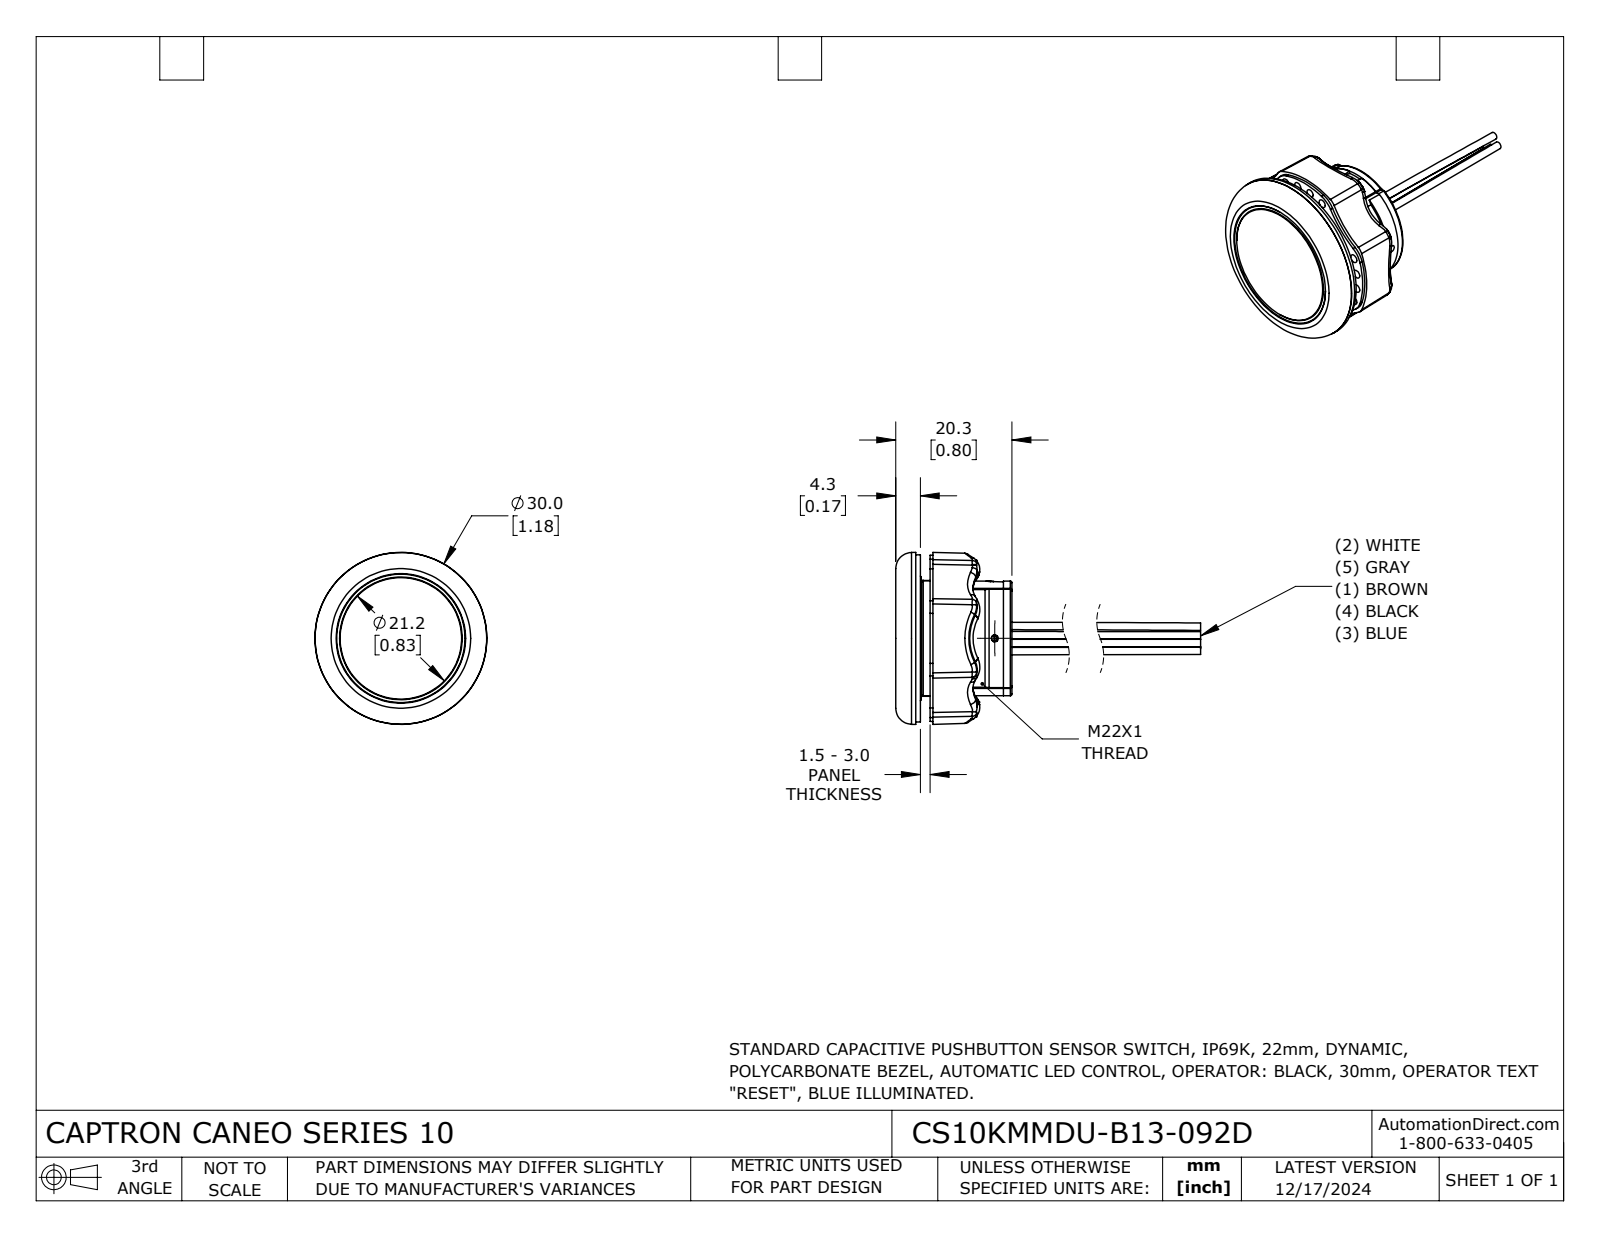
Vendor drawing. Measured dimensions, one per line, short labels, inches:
name: CS10KMMDU-B13-092D
written by: SolidWorks 2024 (CONFIG_CONTROL_DESIGN)
unit: in
bodies: 7 solids, 601 faces (204 planar, 75 cylindrical, 322 other)
size: 2.049 × 1.181 × 1.181
volume: 0.649 in³; area: 9.995 in²
holes: 1× ⌀0.047, 1× ⌀0.827, 1× ⌀0.927
bosses: 1× ⌀1.181, 1× ⌀1.15, 1× ⌀0.72, 1× ⌀0.717
rounds: 8× R0.012, 6× R0.004, 6× R0.01, 6× R0.295, 4× R0.02, 4× R0.039, 4× R0.689, 1× R0.362
face distances: 0.169, 0.63, 0.799, 0.067, 0.563, 0.236, 0.079, 0.551, 0.248, 0.242
